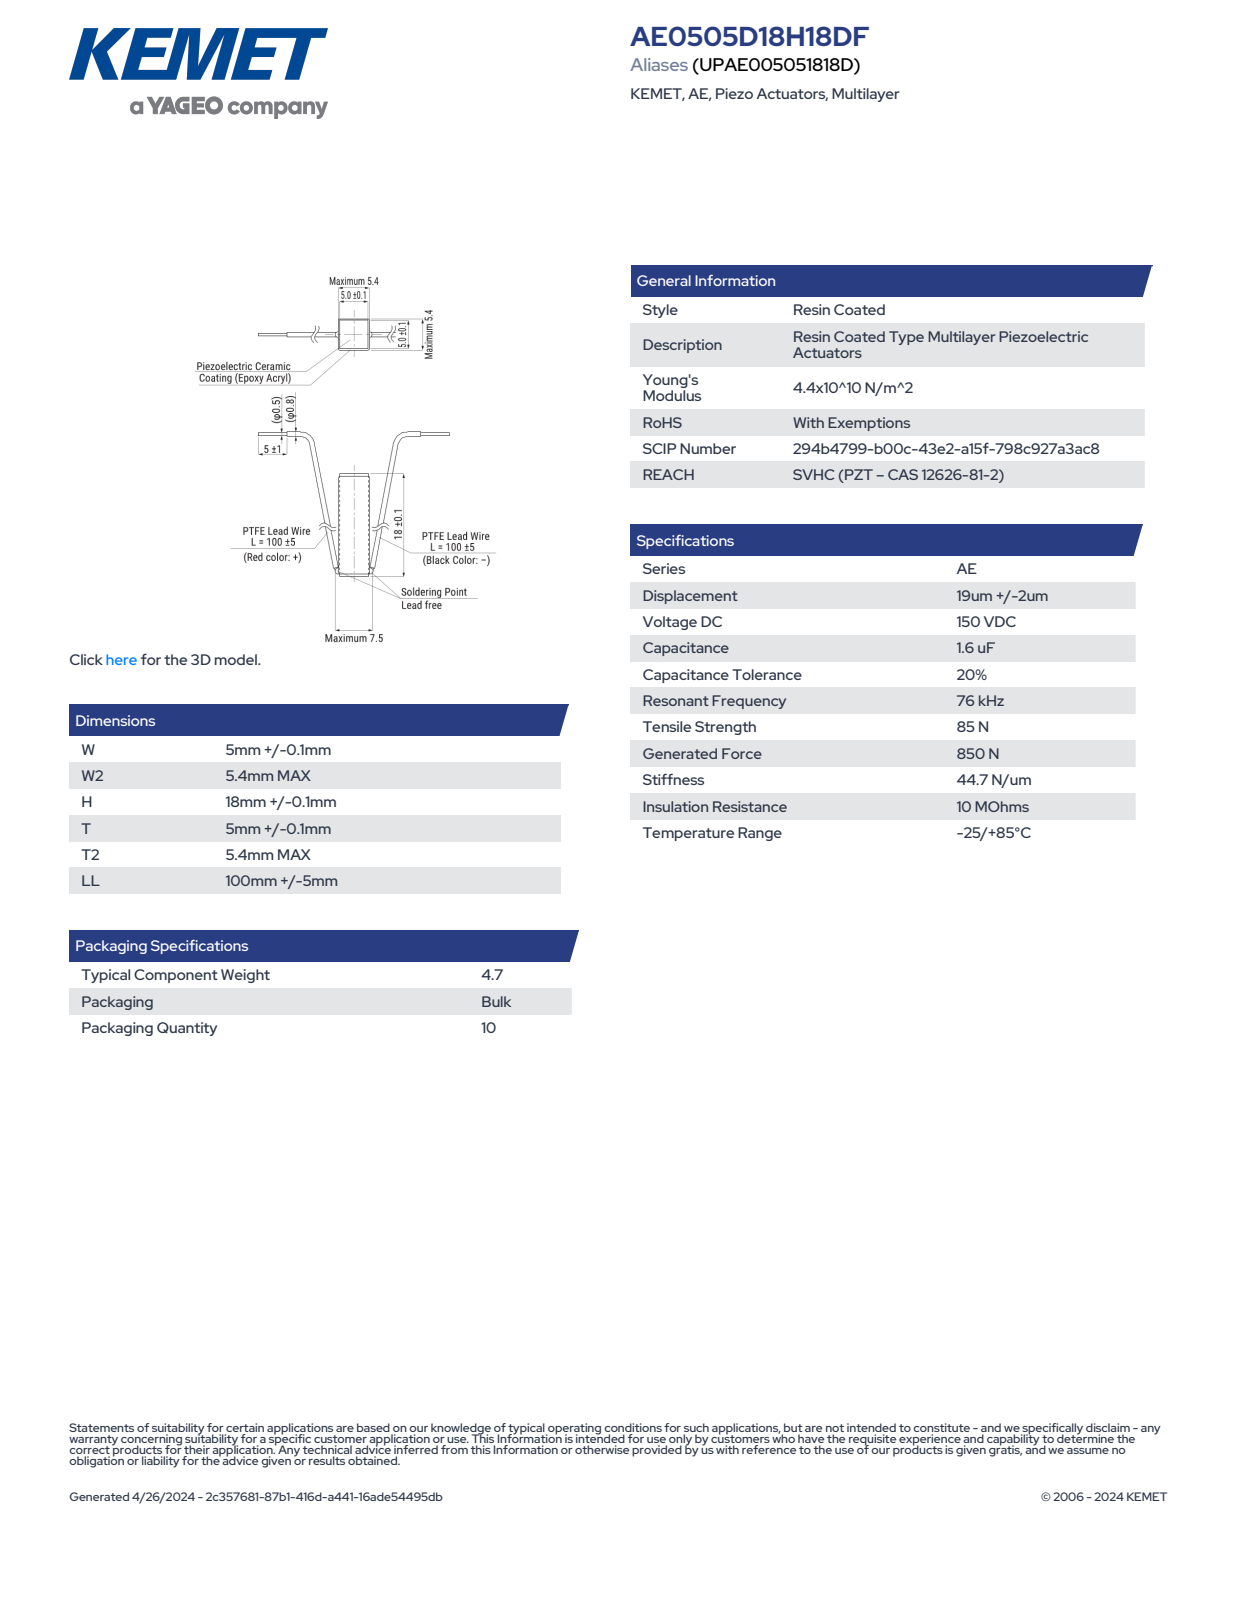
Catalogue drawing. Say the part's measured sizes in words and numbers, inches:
The part is named "AL_KAE1_W5.1W25.4H18.1T5.1T25.4". Its 3-D file was written by "SolidWorks 2014 (AUTOMOTIVE_DESIGN)". It is 4 solids with 93 faces: 85 planar, 8 cylindrical and 0 other. Overall it measures 0.713 by 0.213 by 0.213 inches. Its volume is 0.029 cubic inches and its surface area 0.679 square inches. Partial cylindrical surfaces (rounded edges, fillets, slot ends): 8 of radius 0.006. The main face-to-face distances are 0.201, 0.197, 0.207, 0.193, 0.213, 0.713, 0.287, 0.426, 0.07, 0.643.
